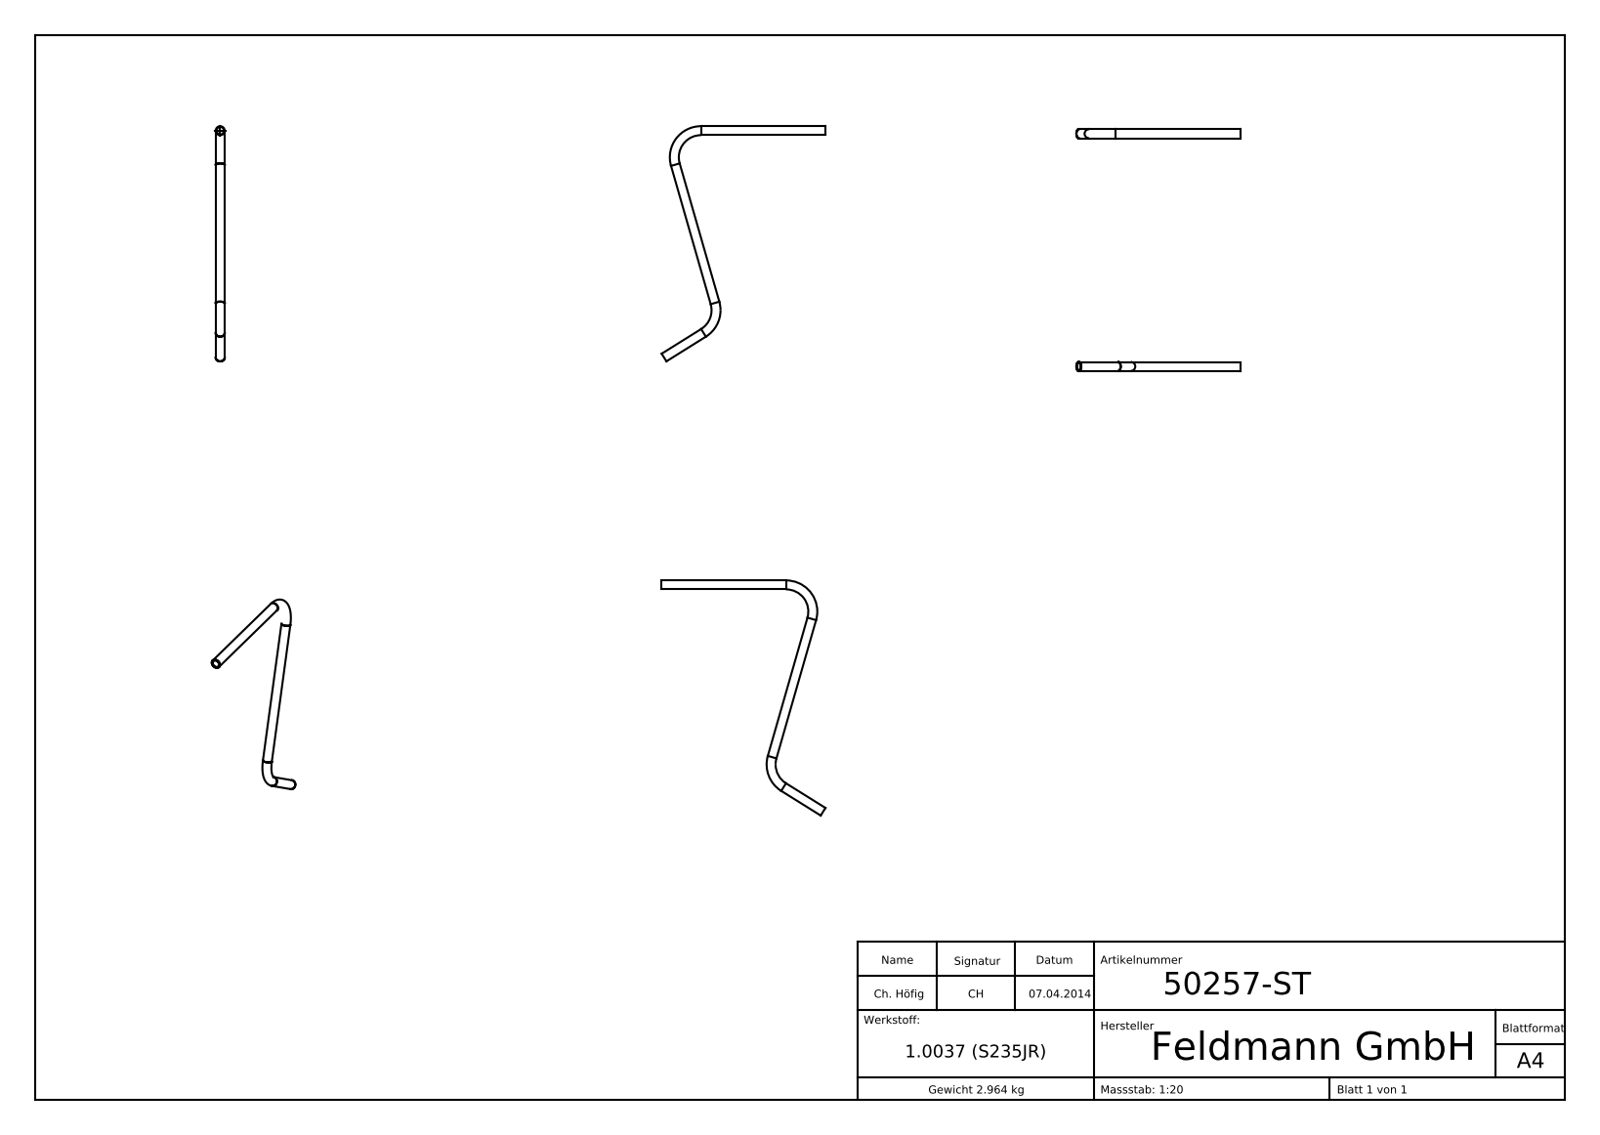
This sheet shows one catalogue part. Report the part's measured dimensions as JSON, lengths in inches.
{"part_name": "50257-ST", "step_written_by": "SolidWorks 2015 (CONFIG_CONTROL_DESIGN)", "units": "inches", "bodies": {"solids": 1, "faces": 236, "planar": 114, "cylindrical": 12, "other": 110}, "overall_size": [34.75, 24.203, 1.327], "volume_in3": 23.19, "surface_area_in2": 454, "round_holes": [[1.122, 3]], "round_bosses_or_shafts": [[1.327, 3]], "face_to_face_distances": [0.02, 0.023, 0.021, 0.017, 0.027, 0.021, 0.019, 0.042, 0.042, 0.046]}
